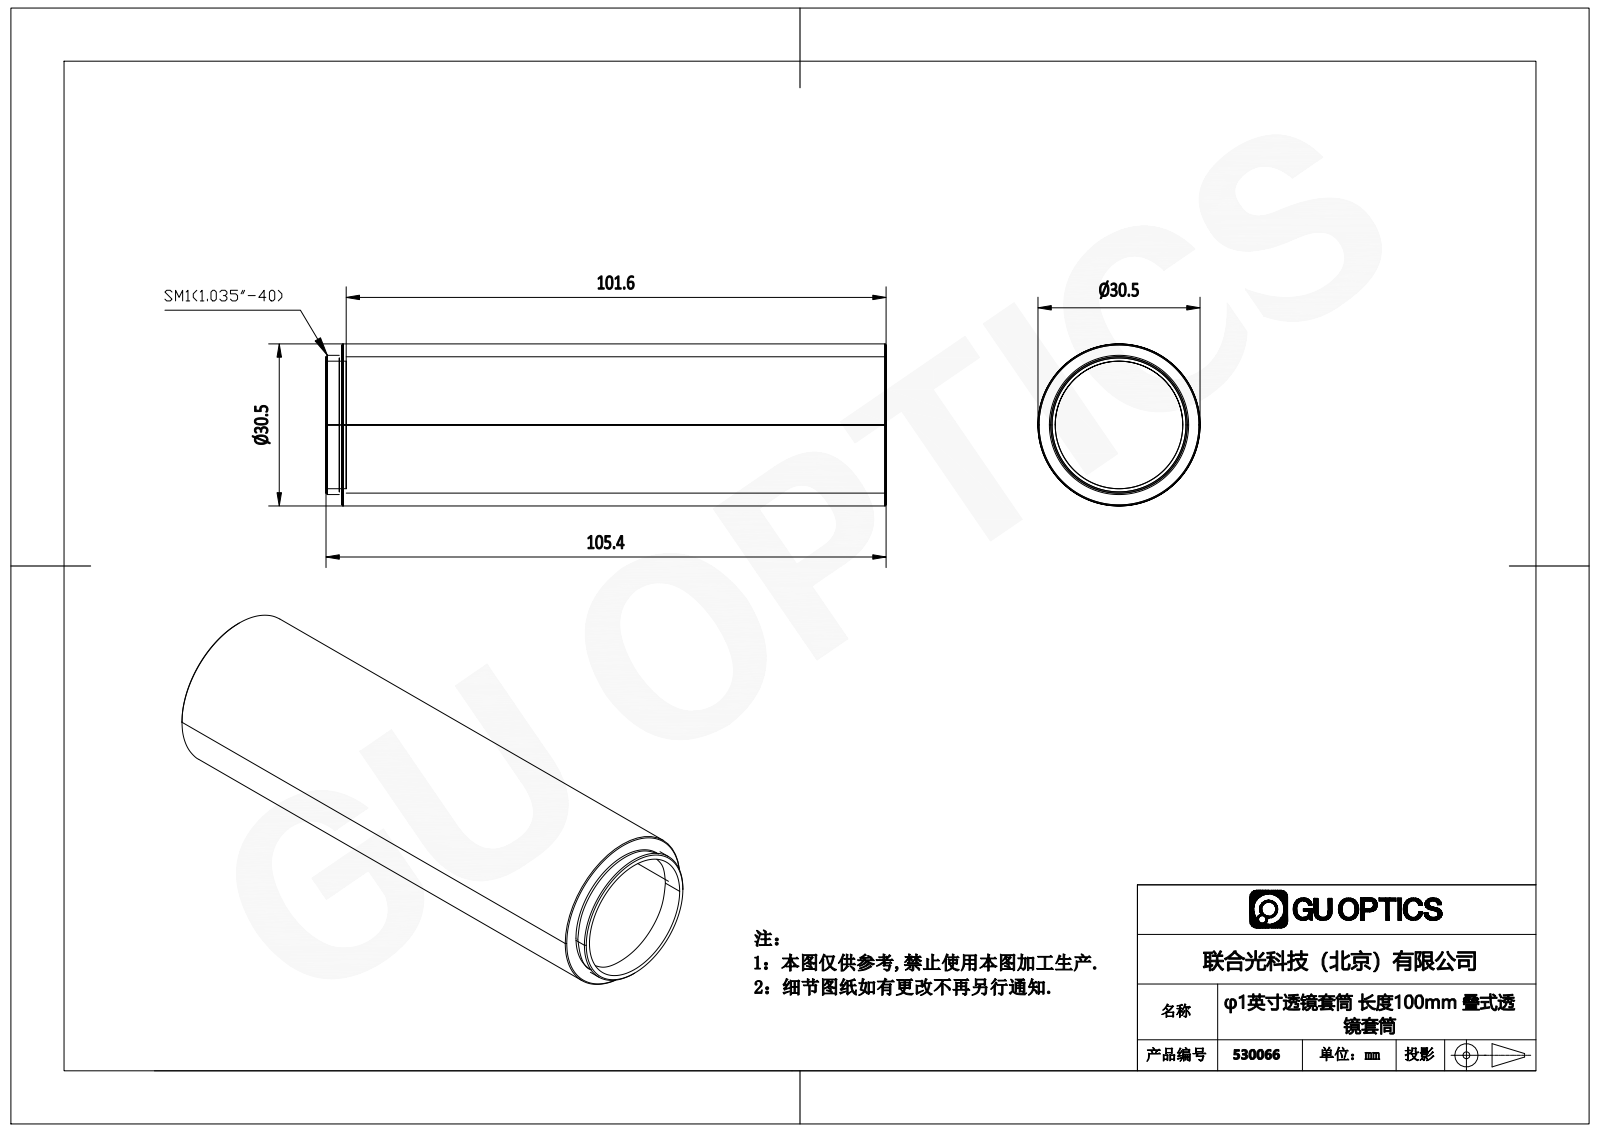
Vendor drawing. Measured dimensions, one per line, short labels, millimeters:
written by: SolidWorks 2018 (AUTOMOTIVE_DESIGN)
unit: mm
bodies: 0 solids, 34 faces (11 planar, 12 cylindrical, 11 other)
size: 105.4 × 30.5 × 30.5
holes: 1× ⌀23.01, 1× ⌀24, 1× ⌀25.65
bosses: 1× ⌀30.5, 1× ⌀26.2, 1× ⌀25.2
face distances: 102.4, 105.4, 3, 0.7, 101.7, 104.7, 1
